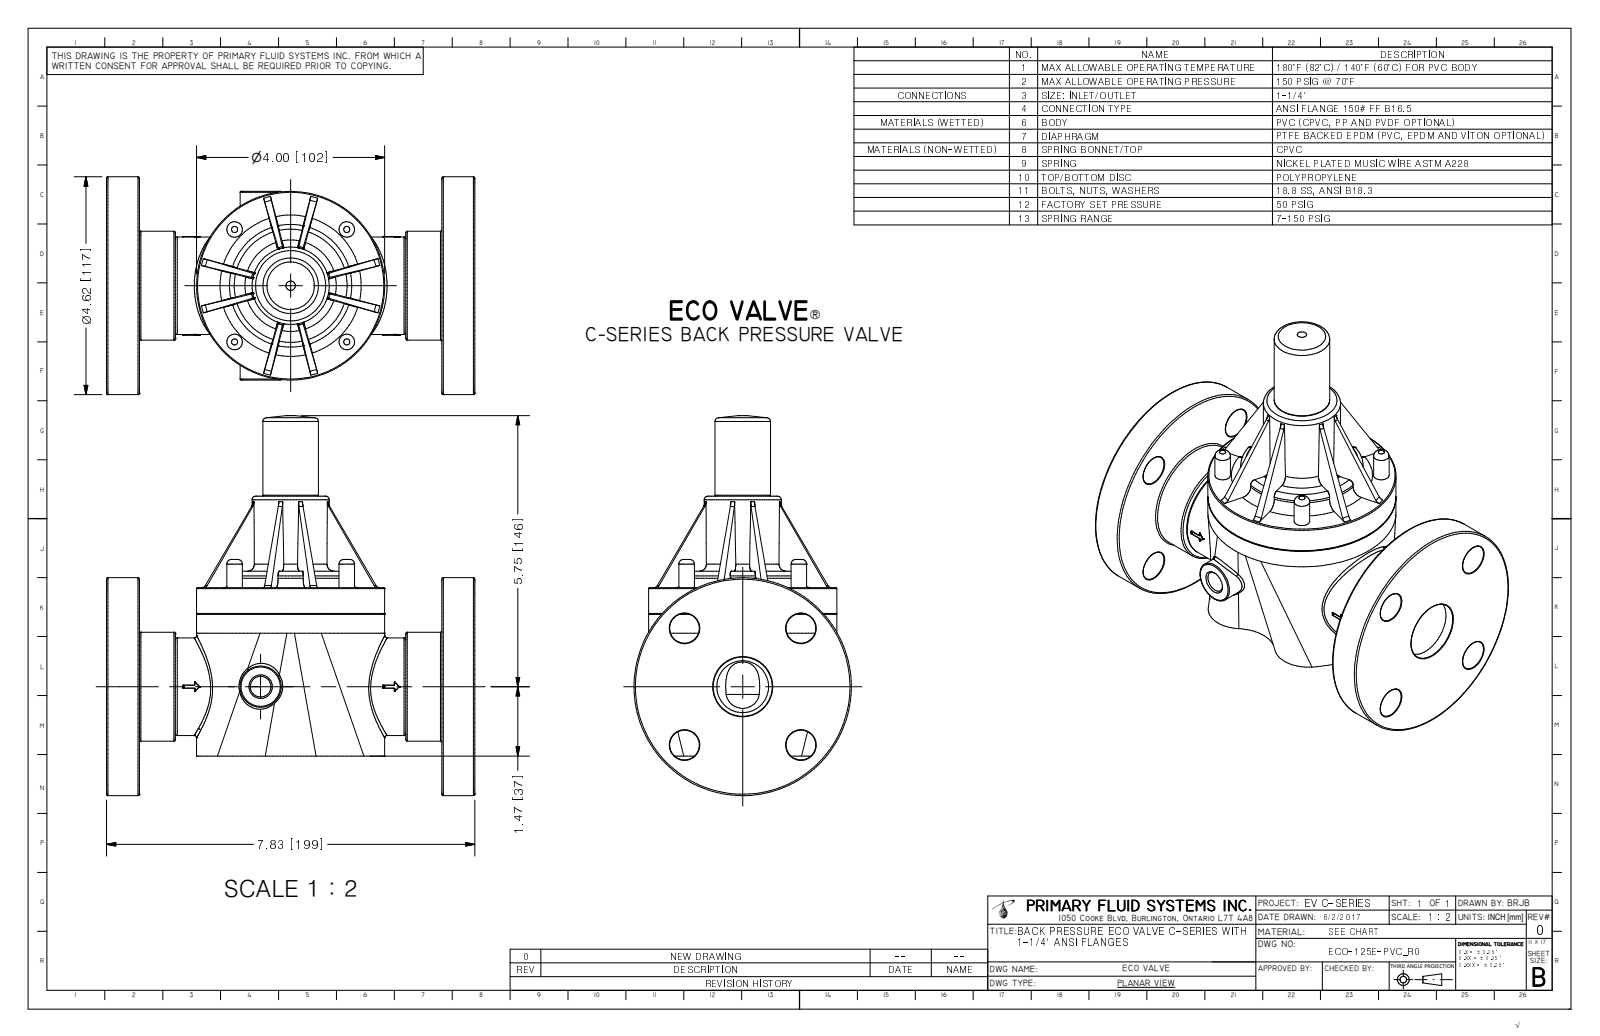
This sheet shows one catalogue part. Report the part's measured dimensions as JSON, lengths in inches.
{"part_name": "ECO-125E-PVC_R0", "step_written_by": "Autodesk Inventor 2009 (AUTOMOTIVE_DESIGN)", "units": "inches", "bodies": {"solids": 1, "faces": 466, "planar": 181, "cylindrical": 101, "other": 184}, "overall_size": [8.059, 7.83, 4.62], "volume_in3": 69.68, "surface_area_in2": 290.6, "round_holes": [[0.23, 4], [0.63, 4], [0.437, 1], [1.255, 1], [1.38, 1]], "round_bosses_or_shafts": [[0.4, 4], [0.33, 4], [4.62, 1], [4, 1], [2.6, 1], [2.311, 1], [2.07, 1], [1.66, 1]], "partial_cylinders_radius": [[0.1, 14], [0.05, 4], [0.225, 4], [0.15, 1], [1.045, 1], [1.559, 1], [1.816, 1]], "face_to_face_distances": [0.7, 7.13, 7.83, 6.43, 3.572, 2.672, 5.157, 1.972, 4.457, 1.465], "hole_center_spacings": [2.385, 1.75, 1.75, 2.475, 2.475, 3.373, 3.5]}
